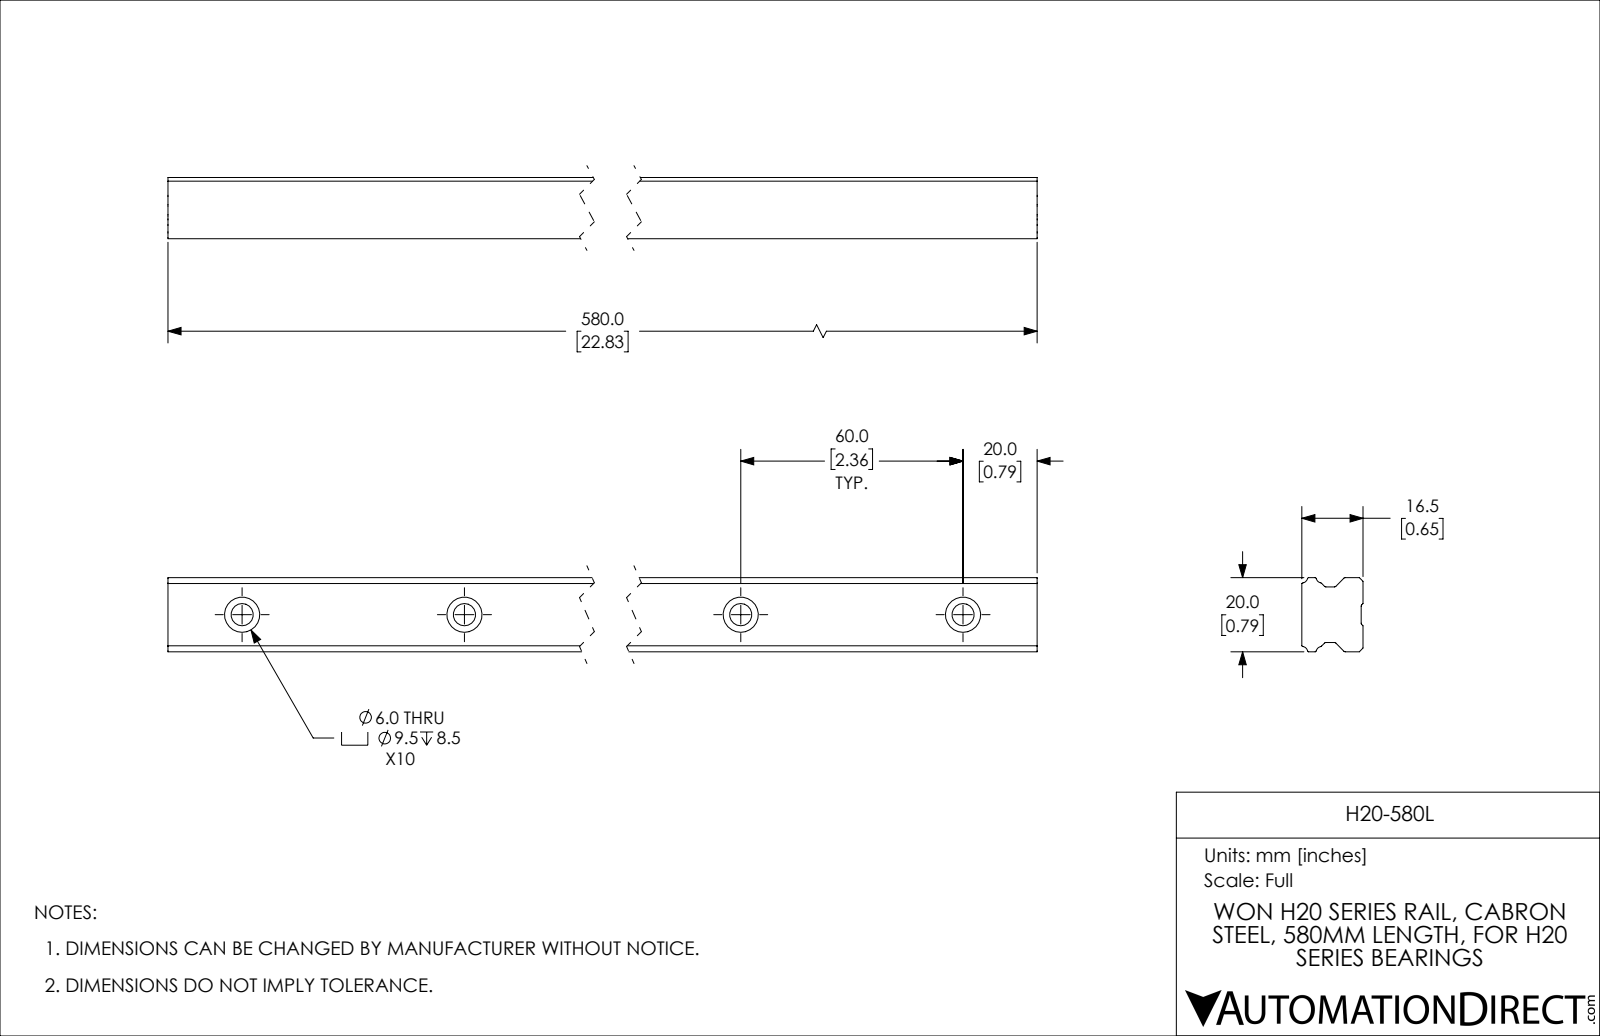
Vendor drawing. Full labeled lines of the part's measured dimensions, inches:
Part name (STEP PRODUCT): H20-580L
STEP written by: SolidWorks 2019 (CONFIG_CONTROL_DESIGN)
Units: inches
Bodies: 1 solid, 140 faces (60 planar, 80 cylindrical, 0 other)
Overall size (bounding box): 22.835 × 0.787 × 0.65
Volume: 9.969 in³ · Surface area: 73.28 in²
Round holes (diameter × count): ⌀0.236 ×10, ⌀0.374 ×10
Partial cylindrical surfaces — rounded edges, fillets, slot ends (radius × count): R0.02 ×12, R0.012 ×4, R0.063 ×4
Main face-to-face distances: 0.65, 0.787, 0.098, 0.689, 0.02, 0.63, 0.326, 0.591, 0.334, 0.668
Hole centre spacings: 2.362, 4.724, 7.087, 9.449, 11.811, 14.173, 16.535, 18.898
